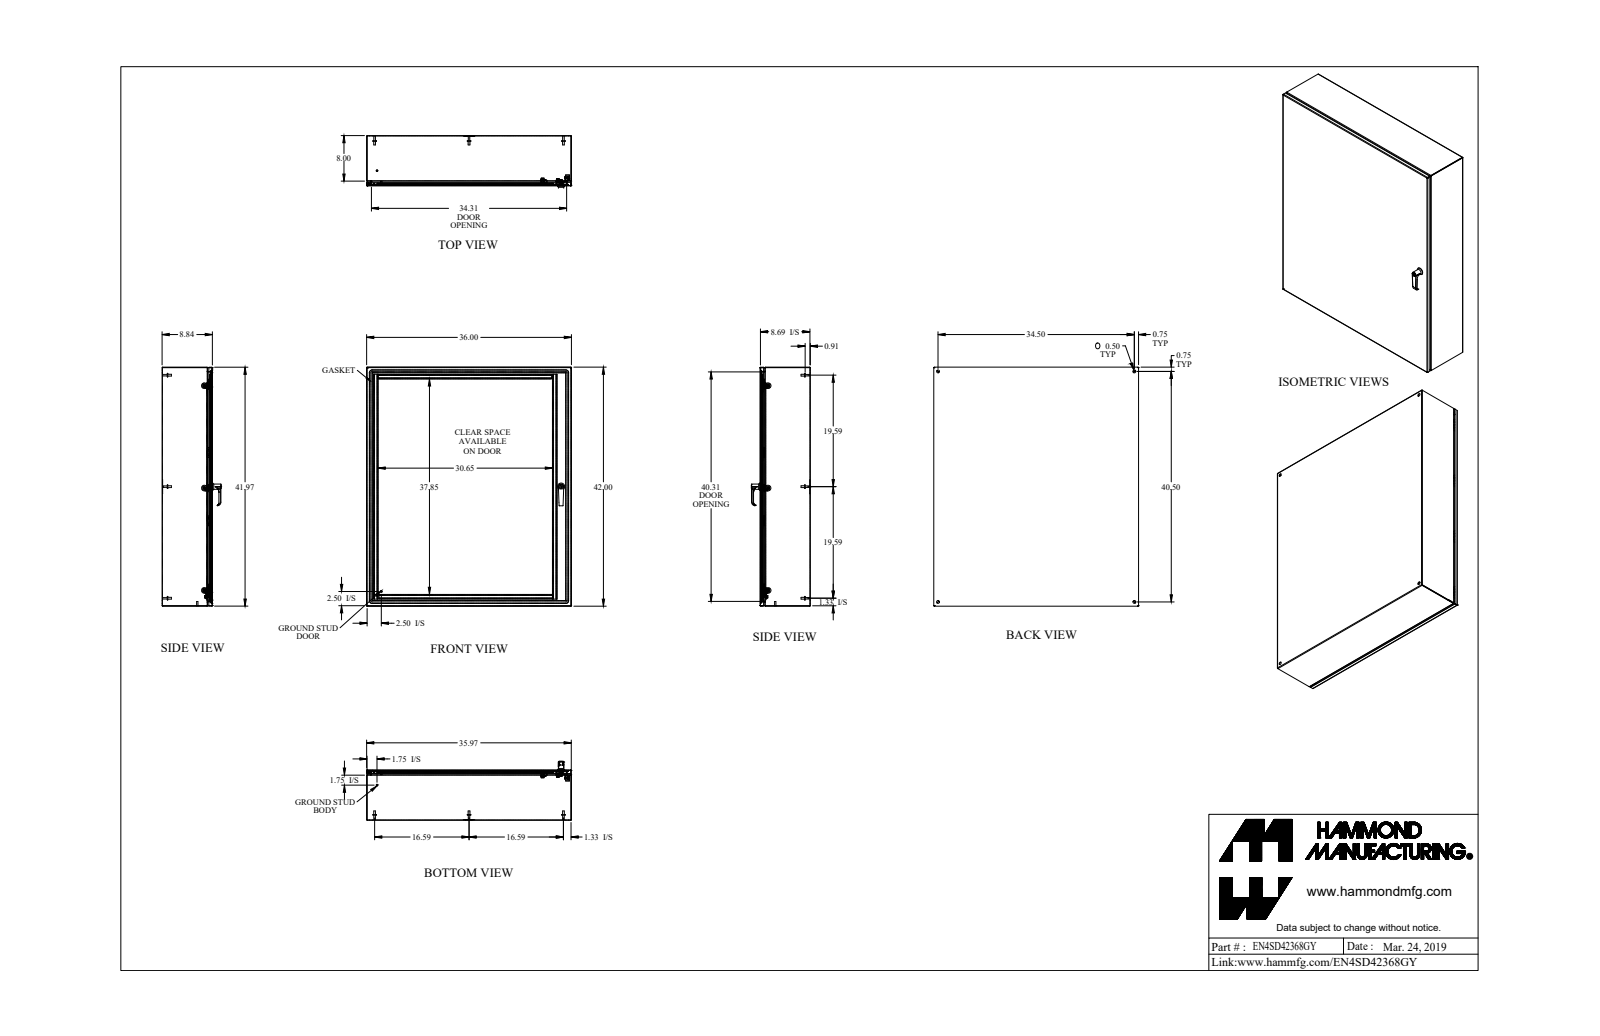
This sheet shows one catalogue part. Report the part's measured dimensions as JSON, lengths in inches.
{"part_name": "EN4SD42368GY_Default", "step_written_by": "SolidWorks 2019 (CONFIG_CONTROL_DESIGN)", "units": "inches", "bodies": {"solids": 61, "faces": 1733, "planar": 757, "cylindrical": 638, "other": 338}, "overall_size": [42, 36, 10.367], "volume_in3": 364.3, "surface_area_in2": 10193, "round_holes": [[0.176, 6], [0.196, 4], [0.5, 4], [0.25, 3], [0.265, 3], [0.413, 3], [0.256, 2], [0.313, 2], [0.394, 2], [0.172, 1], [0.24, 1], [0.242, 1]], "round_bosses_or_shafts": [[0.313, 8], [0.27, 8], [0.625, 7], [0.25, 7], [0.156, 6], [0.375, 5], [1, 3], [0.63, 2]], "partial_cylinders_radius": [[0.043, 24], [0.081, 24], [0.036, 20], [0.108, 20], [0.062, 17], [0.03, 15], [0.094, 10], [0.016, 9]], "face_to_face_distances": [0.072, 8.765, 8.693, 8.837, 35.928, 41.928, 35.856, 36, 41.856, 42], "hole_center_spacings": [0.787, 2.507, 18, 33.504, 34.5, 35.969, 38.25, 40.5]}
